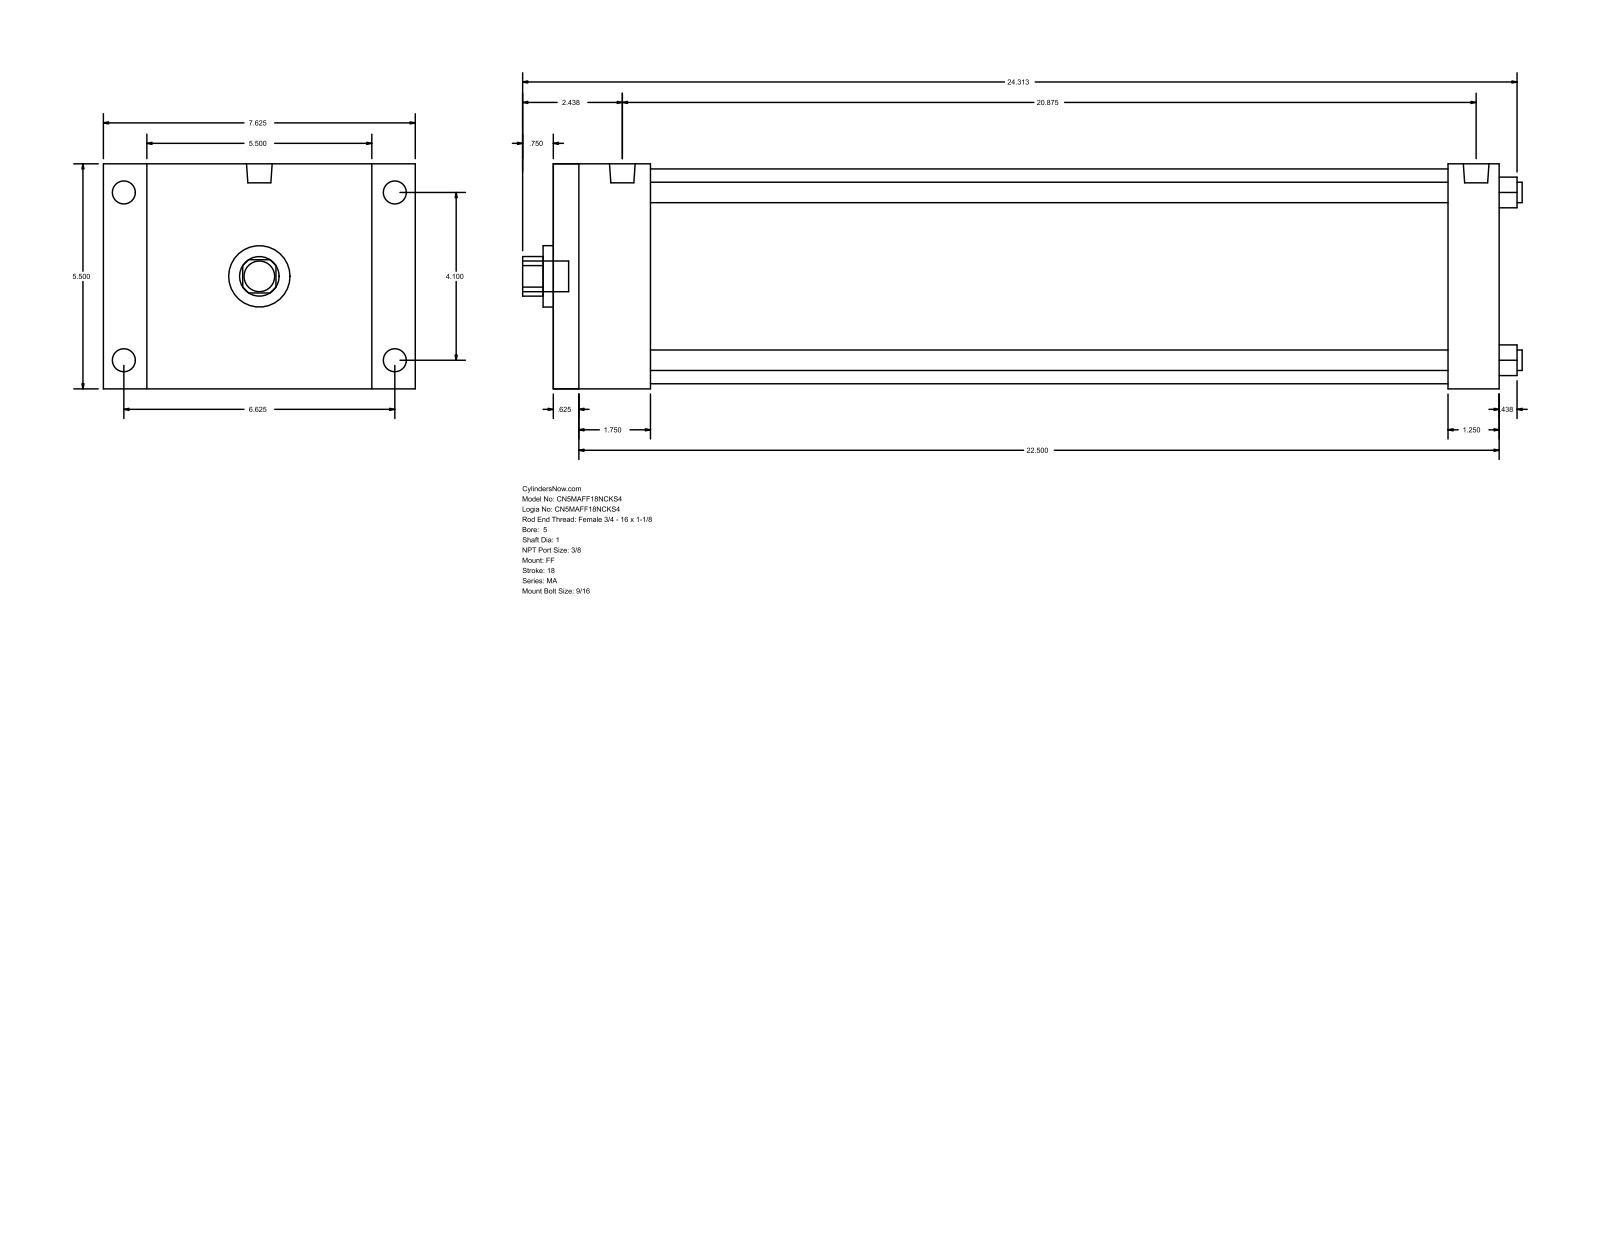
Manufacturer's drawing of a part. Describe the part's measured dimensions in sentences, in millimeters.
The part is named "MA_FF__0500_1". Its 3-D file was written by "GSSL Pune (CONFIG_CONTROL_DESIGN)". It is 0 solids with 92 faces: 64 planar, 28 cylindrical and 0 other. Overall it measures 620.71 by 193.68 by 139.7 millimeters. Round holes: 4 of diameter 12.7, 1 of diameter 25.4, 1 of diameter 38.1, 1 of diameter 133.35. Round bosses or shafts: 4 of diameter 14.29, 4 of diameter 11.11, 2 of diameter 15.93, 1 of diameter 19.05. Partial cylindrical surfaces (rounded edges, fillets, slot ends): 1 of radius 12.29. The main face-to-face distances are 139.7, 587.37, 15.87, 571.5, 555.62, 539.75, 31.75, 60.33, 44.46, 495.29. The hole center spacings are 73.64, 104.14, 147.28.
